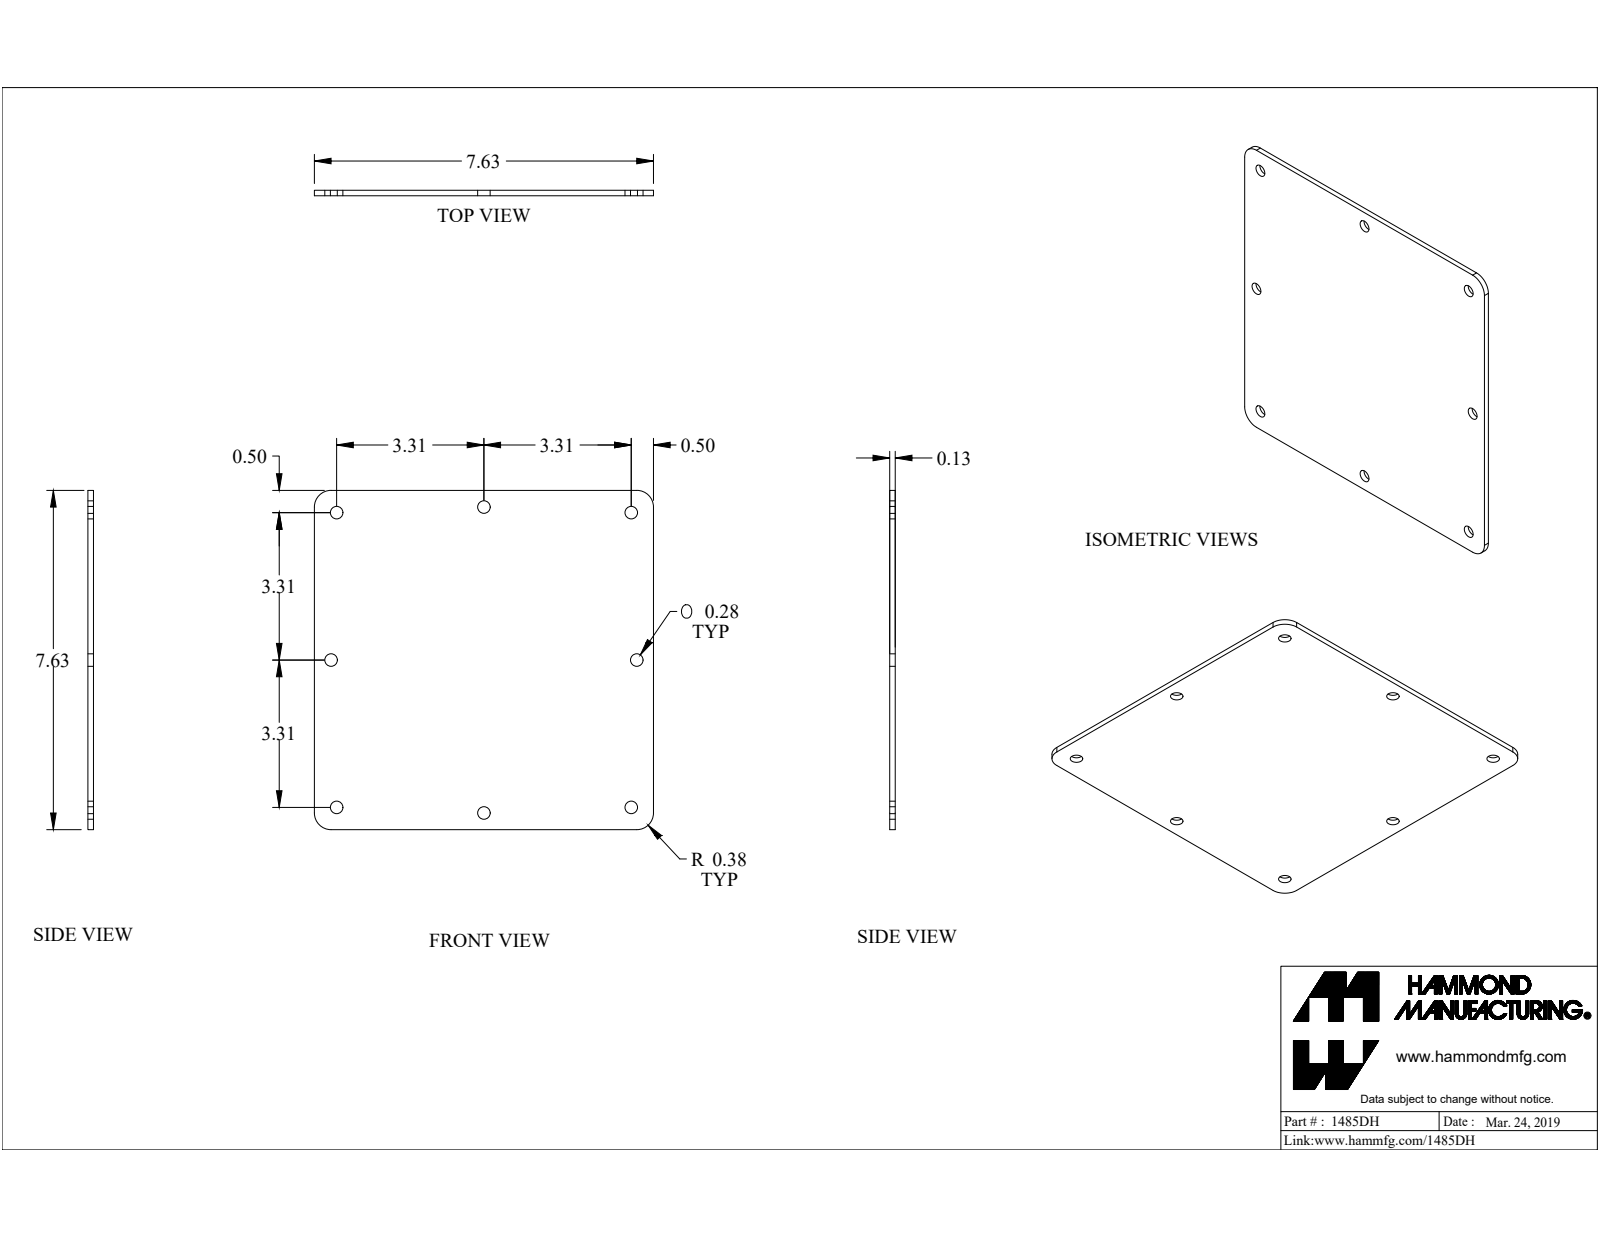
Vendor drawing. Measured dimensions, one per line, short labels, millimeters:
name: 1485DH
written by: SolidWorks 2019 (CONFIG_CONTROL_DESIGN)
unit: mm
bodies: 1 solid, 18 faces (6 planar, 12 cylindrical, 0 other)
size: 193.7 × 193.7 × 3.2
volume: 117 800 mm³; area: 77 230 mm²
holes: 8× ⌀7.1
rounds: 4× R9.5
face distances: 3.2, 193.7
hole spacings: 84.2, 191, 123.5, 168.3, 174.6, 238
